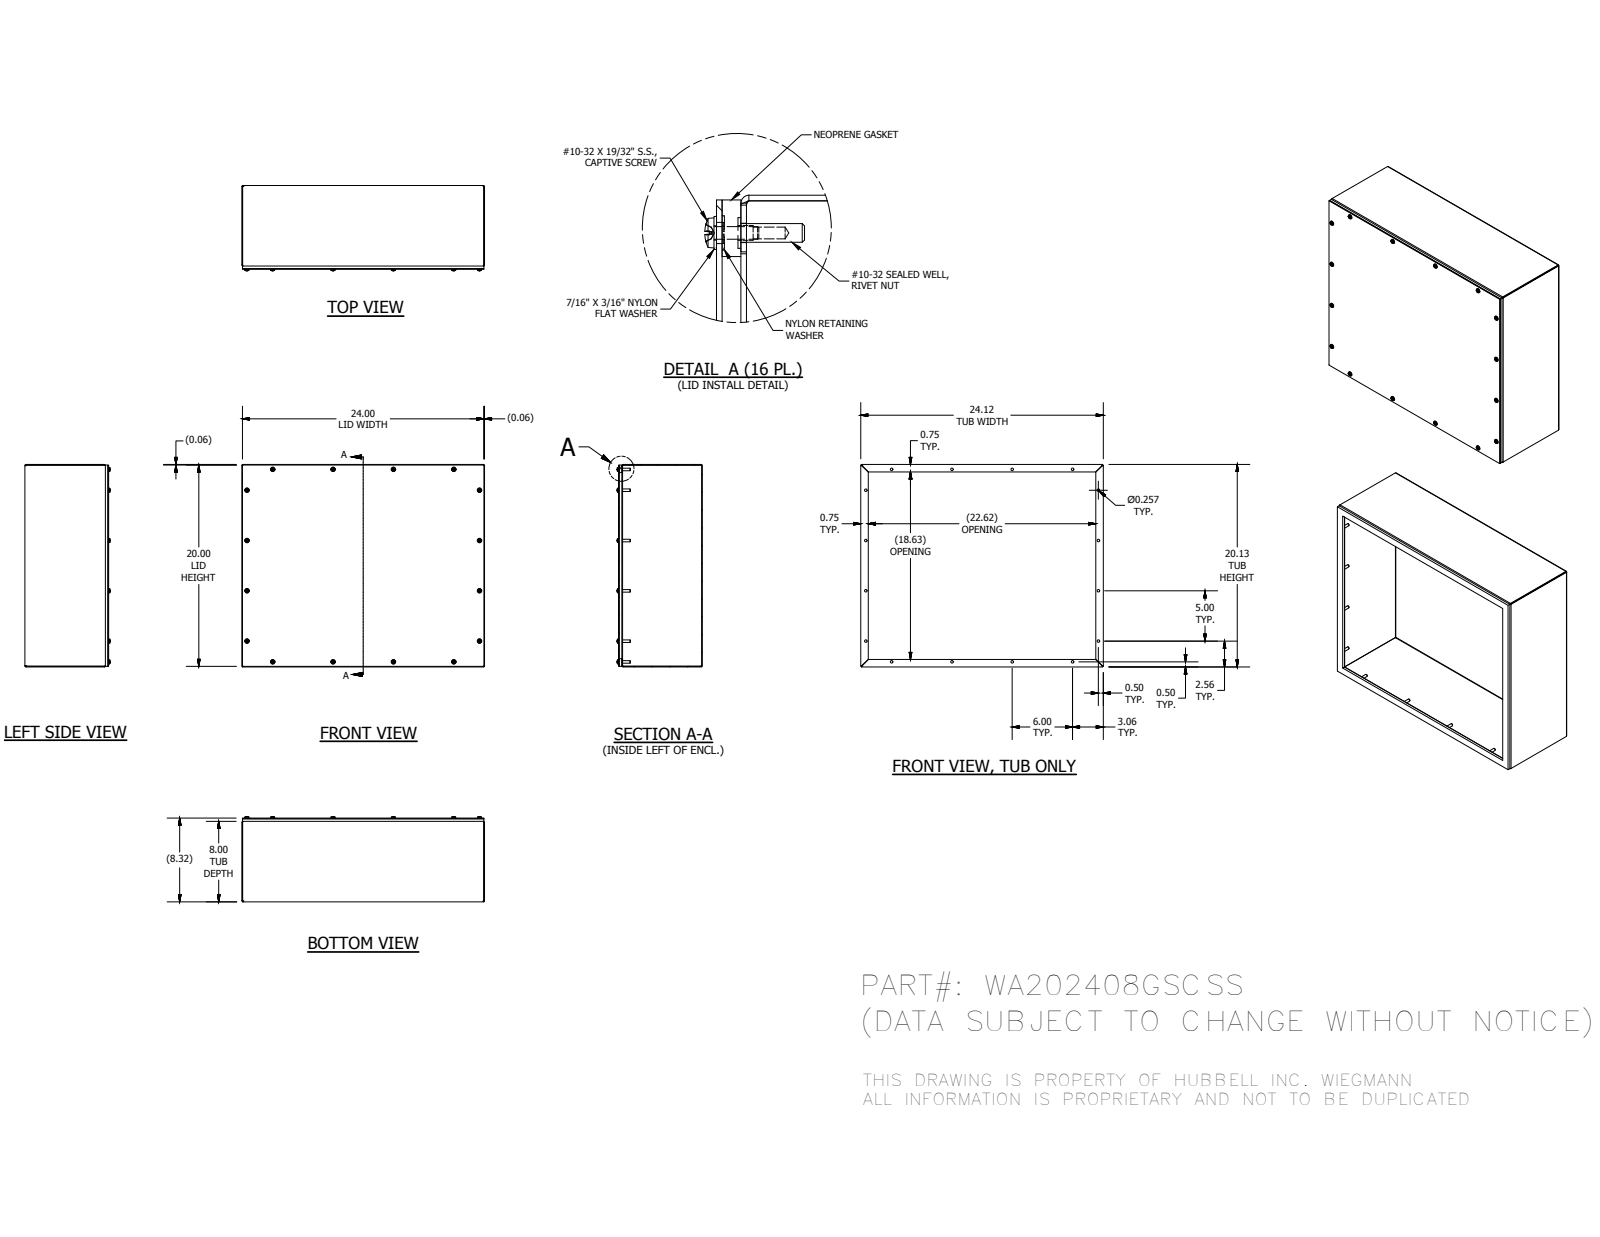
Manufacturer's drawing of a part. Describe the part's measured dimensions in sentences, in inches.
The part is named "WA202408GSCSSBKP; WA2024GSCSSLID; 37210; 39035 (+4 more)". Its 3-D file was written by "Autodesk Inventor 2016 (AUTOMOTIVE_DESIGN)". It is 67 solids with 1382 faces: 758 planar, 272 cylindrical and 352 other. Overall it measures 24.125 by 20.125 by 8.478 inches. Its volume is 143.6 cubic inches and its surface area 3 658 square inches. Round holes: 16 of diameter 0.156, 16 of diameter 0.188, 16 of diameter 0.196, 16 of diameter 0.257, 16 of diameter 0.278, 16 of diameter 0.281. Round bosses or shafts: 16 of diameter 0.453, 16 of diameter 0.437, 16 of diameter 0.406, 16 of diameter 0.248, 16 of diameter 0.167. Partial cylindrical surfaces (rounded edges, fillets, slot ends): 16 of radius 0.089, 12 of radius 0.031, 8 of radius 0.07, 8 of radius 0.105. The main face-to-face distances are 0.074, 8.25, 8.324, 8.176, 20.051, 24.051, 20.125, 19.977, 7.926, 0.324. The hole center spacings are 5, 6, 20.044, 23.659, 3.289, 7.513, 8.807, 10.
